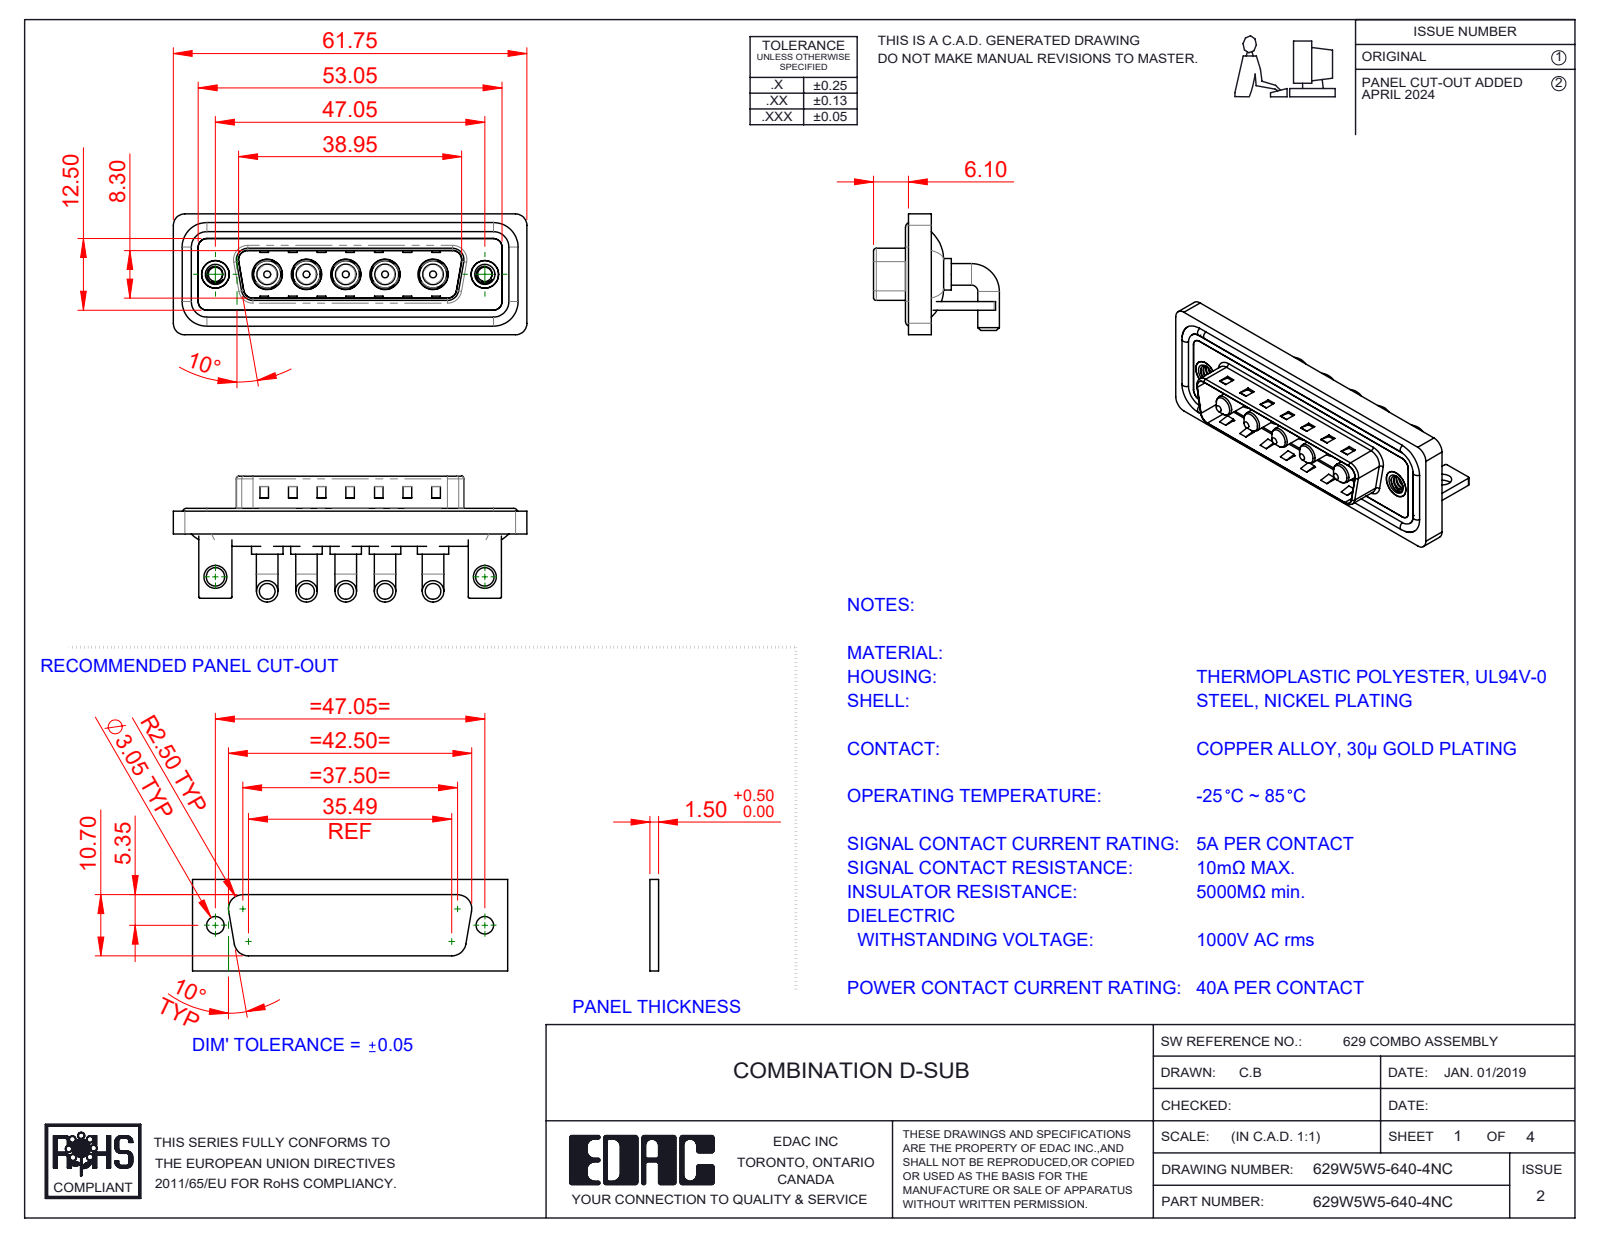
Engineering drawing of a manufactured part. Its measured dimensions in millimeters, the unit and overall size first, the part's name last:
Units: millimetres
Overall size (bounding box): 61.75 × 21.98 × 21.1
Round holes (diameter × count): ⌀4.85 ×5, ⌀5.3 ×5, ⌀2.5 ×2, ⌀3.2 ×2, ⌀4 ×2, ⌀4.8 ×2, ⌀5 ×2
Round bosses / shafts (diameter × count): ⌀3.75 ×10, ⌀5.5 ×5, ⌀5.2 ×5, ⌀4.75 ×5, ⌀3.6 ×5, ⌀1.6 ×4, ⌀4.9 ×2
Partial cylindrical surfaces — rounded edges, fillets, slot ends (radius × count): R2 ×19, R1.5 ×18, R0.25 ×16, R0.5 ×9, R1.6 ×8, R2.1 ×5, R0.6 ×4, R0.65 ×4
Main face-to-face distances: 0.4, 1.5, 2.9, 0.8, 2.1, 3.7, 1.1, 4.5, 4.1, 1.2
Hole centre spacings: 6.86, 13.73, 47.05, 6.85, 6.87, 8.37, 8.38, 9.04
Volume: 8 439 mm³ · Surface area: 13 079 mm²
Bodies: 19 solids, 736 faces (279 planar, 311 cylindrical, 146 other)
Part name (STEP PRODUCT): 629Combo Shell Front_25 Contacts; Power Pin_40A RA; 629Combo Shell Rear_25 Contacts; 629Combo Housing_5W5 (+4 more)
STEP written by: SolidWorks 2023 (CONFIG_CONTROL_DESIGN)
